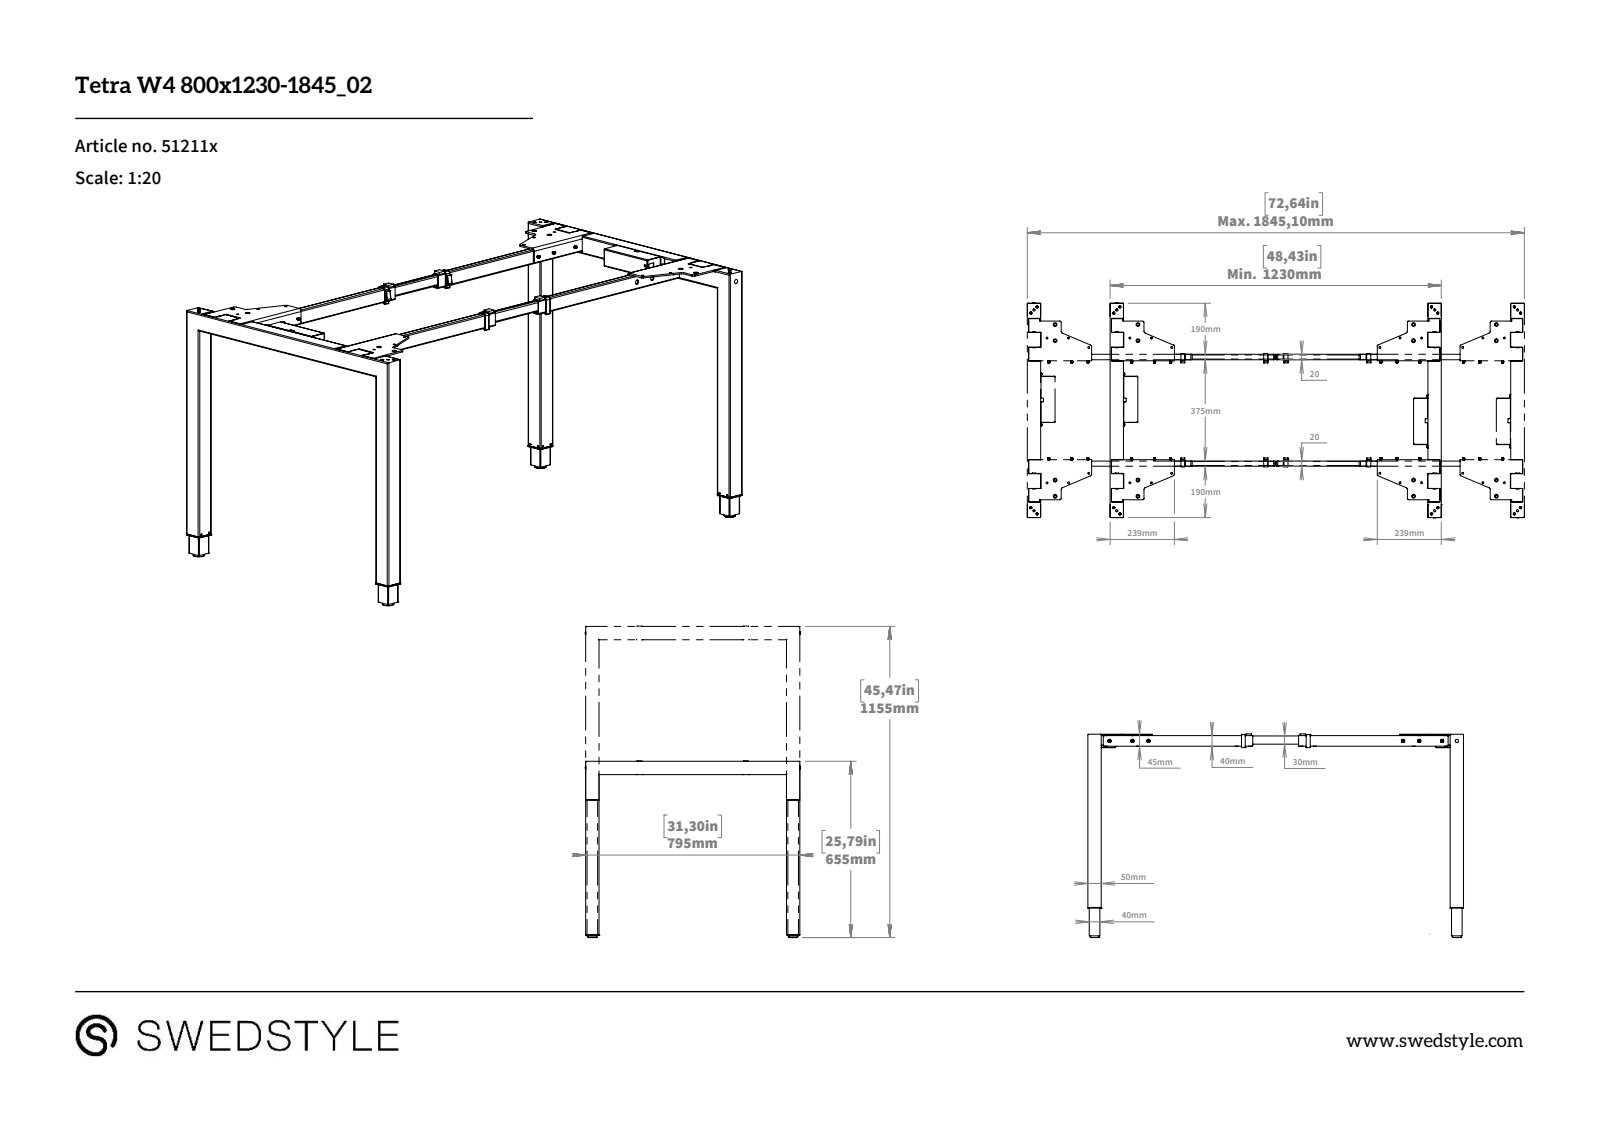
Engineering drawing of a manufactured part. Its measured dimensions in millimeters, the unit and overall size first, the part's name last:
Units: millimetres
Overall size (bounding box): 1395.2 × 799 × 705.8
Round holes (diameter × count): ⌀5 ×12, ⌀7 ×12, ⌀6.8 ×8, ⌀9 ×8, ⌀6 ×4, ⌀8 ×4, ⌀12 ×4, ⌀4 ×2, ⌀4.2 ×2
Round bosses / shafts (diameter × count): ⌀6 ×6, ⌀10.5 ×4, ⌀7.5 ×4
Partial cylindrical surfaces — rounded edges, fillets, slot ends (radius × count): R3 ×40, R2 ×20, R0.5 ×18, R2.5 ×16, R5 ×14, R1.5 ×8, R2.3 ×8, R3.5 ×8
Main face-to-face distances: 50, 2, 395, 1345, 18, 4, 745, 1295, 1395, 46
Hole centre spacings: 10, 31.62, 50.99, 58.31, 60, 70.71, 80, 82.76
Bodies: 0 solids, 1062 faces (416 planar, 390 cylindrical, 256 other)
Part name (STEP PRODUCT): 51211x_Tetra W4 800x1230-1845_2020
STEP written by: SolidWorks 2019 (CONFIG_CONTROL_DESIGN)
